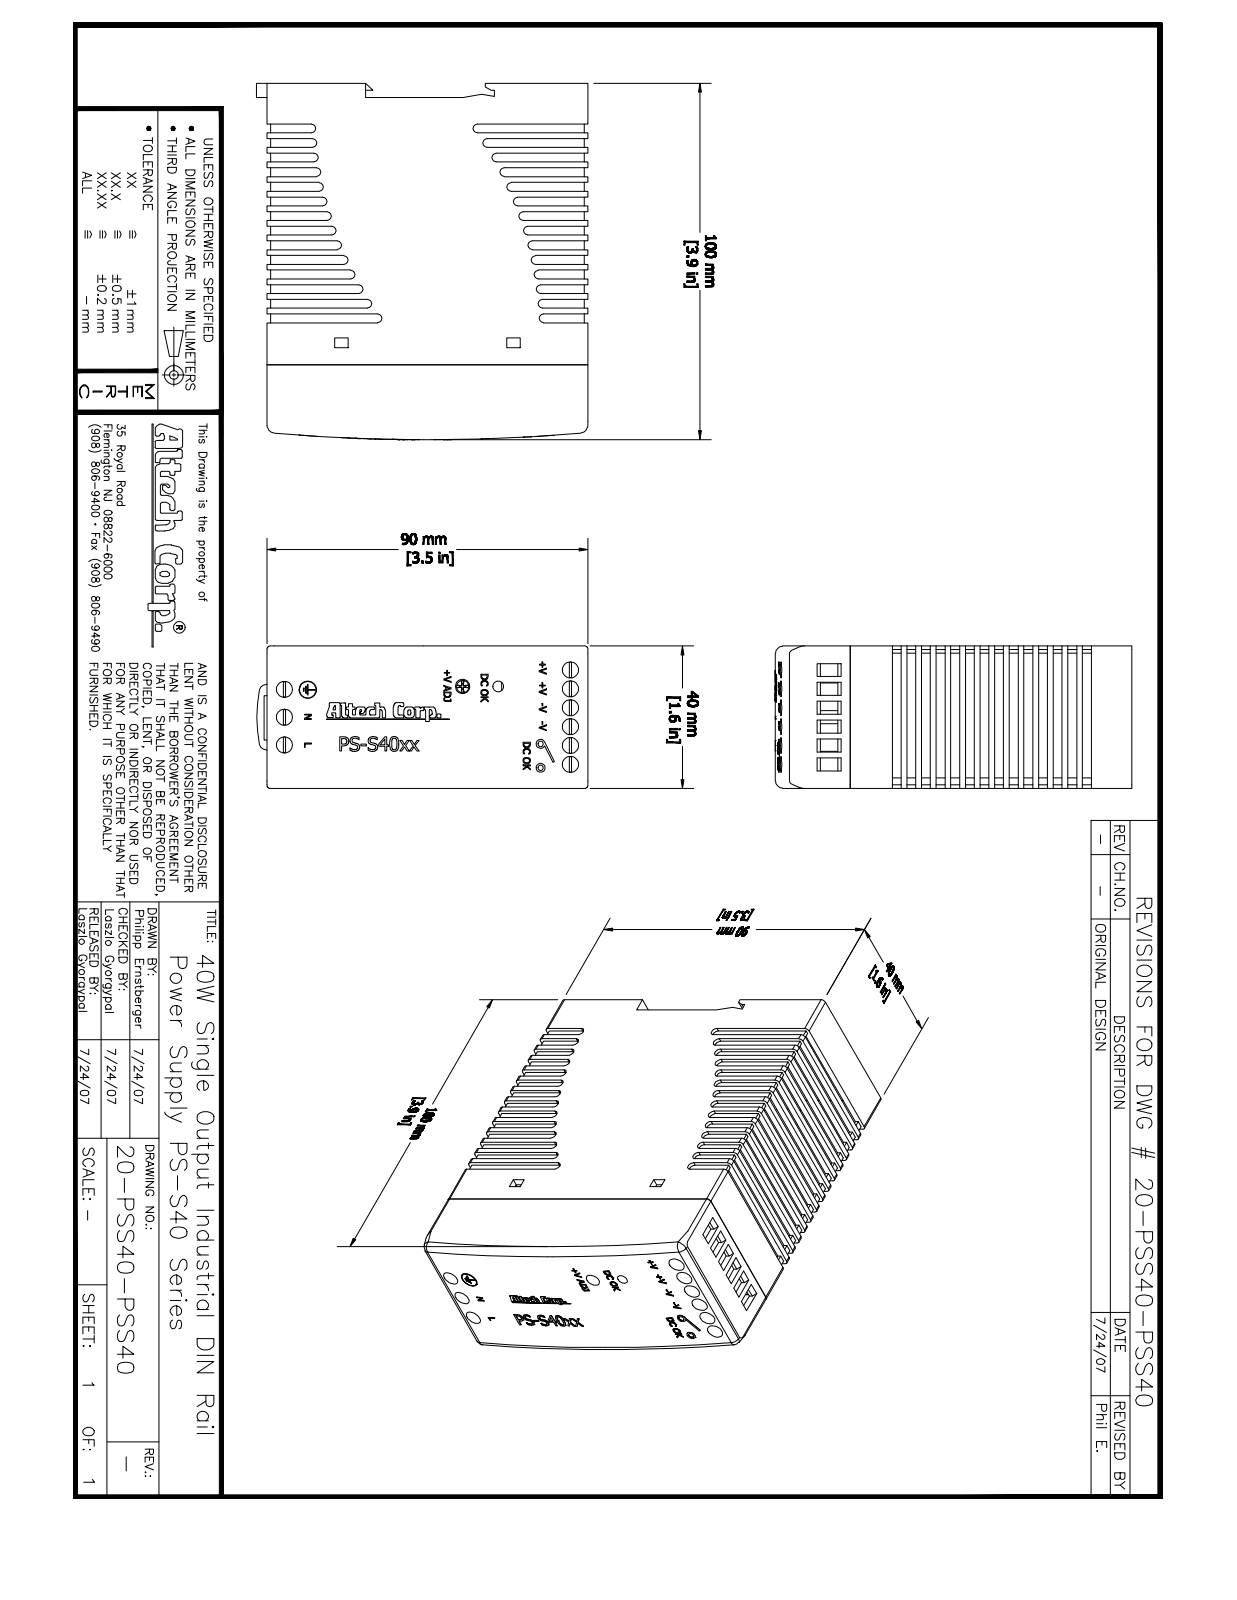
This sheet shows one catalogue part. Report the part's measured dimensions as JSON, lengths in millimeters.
{"part_name": "PS-S40xx; box; front; interlock (+2 more)", "step_written_by": "Autodesk Inventor 2008 (AUTOMOTIVE_DESIGN)", "units": "millimeters", "bodies": {"solids": 13, "faces": 1386, "planar": 775, "cylindrical": 371, "other": 240}, "overall_size": [100.01, 92.92, 40], "volume_mm3": 55873, "surface_area_mm2": 69896, "round_holes": [[4.5, 9], [1.5, 2], [3, 1], [4, 1], [4.6, 1]], "round_bosses_or_shafts": [[2.5, 11], [4.8, 9], [2.22, 9], [3.5, 2], [4.9, 1], [4.5, 1], [2, 1]], "partial_cylinders_radius": [[1.25, 56], [2, 10], [1, 4], [0.12, 2], [0.12, 2], [0.12, 2], [0.13, 2], [0.14, 2]], "face_to_face_distances": [2, 38, 36, 40, 1, 88, 4, 37, 39, 4.1], "hole_center_spacings": [5.3, 10.6, 15.9, 7.8, 21.2, 80.16, 80.2, 80.33]}
